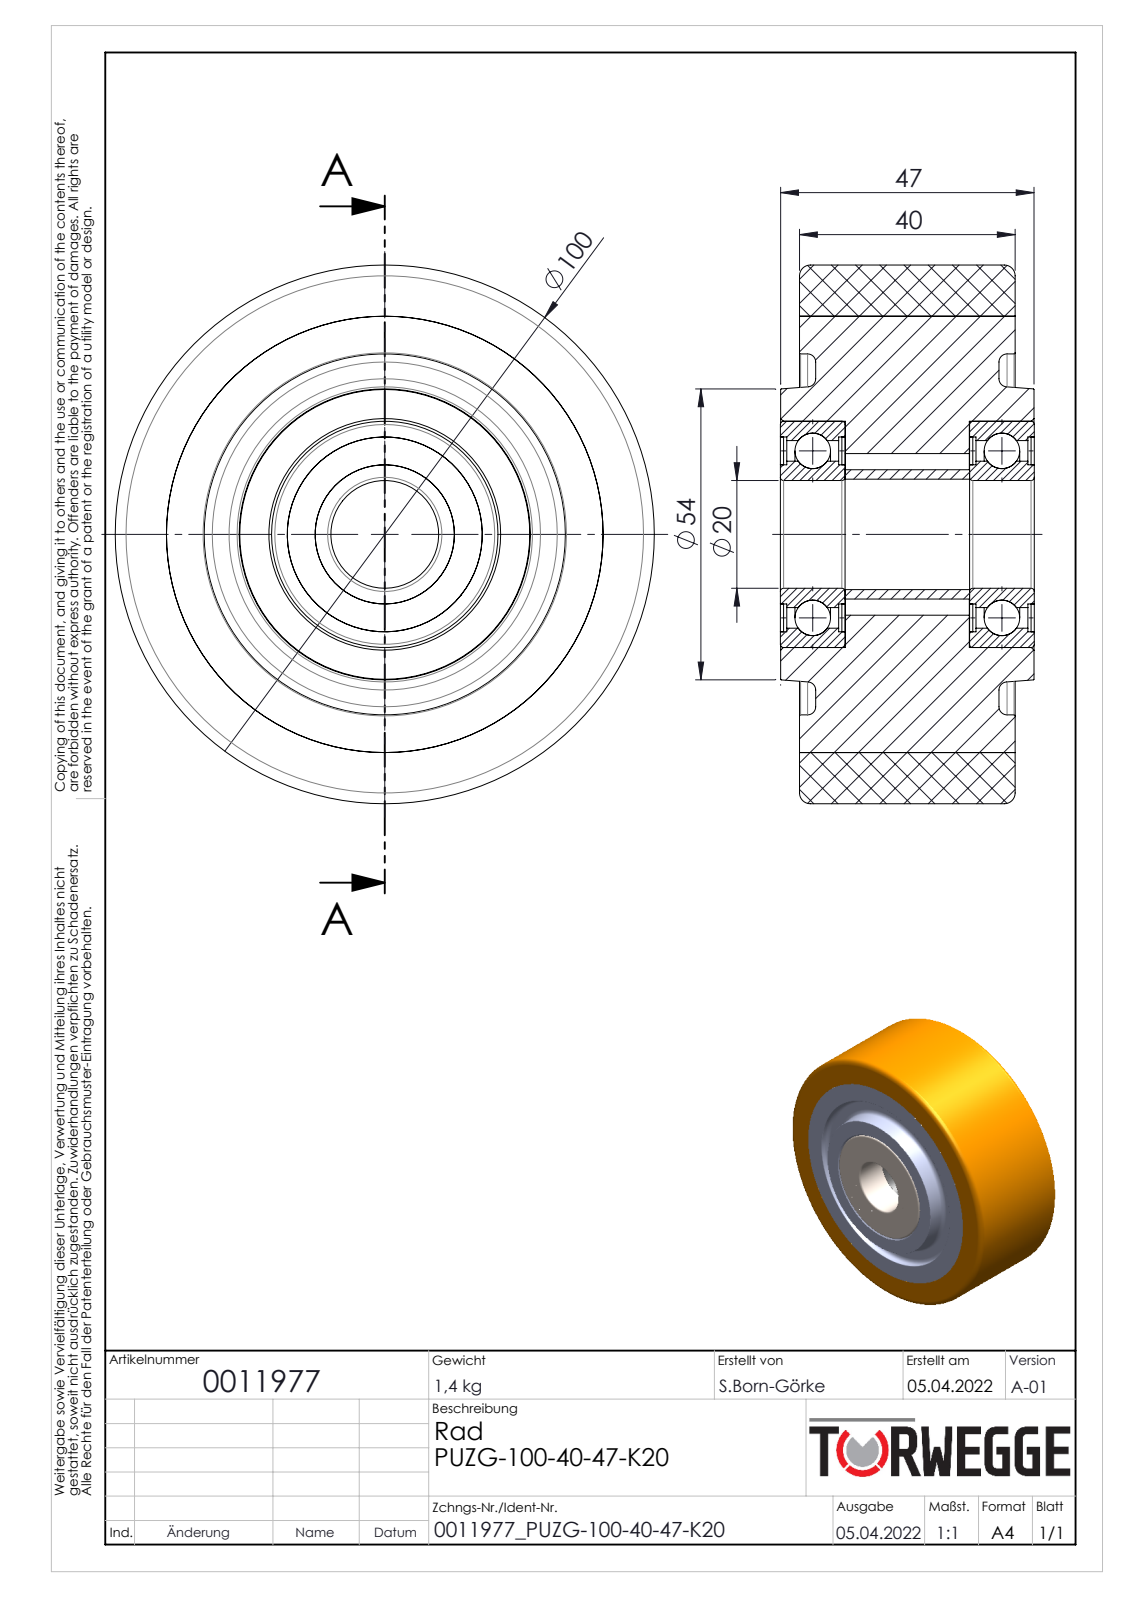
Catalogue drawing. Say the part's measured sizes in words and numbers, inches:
The part is named "0011977". Its 3-D file was written by "SolidWorks 2020 (AUTOMOTIVE_DESIGN)". It is 13 solids with 176 faces: 36 planar, 76 cylindrical and 64 other. Overall it measures 3.937 by 3.937 by 1.854 inches. Its volume is 18.21 cubic inches and its surface area 122.5 square inches. Round holes: 1 of diameter 0.787, 1 of diameter 0.807, 1 of diameter 1.017, 1 of diameter 1.181, 1 of diameter 1.371, 1 of diameter 1.424, 1 of diameter 1.654, 1 of diameter 2.638, 1 of diameter 3.189. Round bosses or shafts: 1 of diameter 3.937, 1 of diameter 1.07, 1 of diameter 0.945. The main face-to-face distances are 1.575, 0.472, 1.382, 1.38, 0.333, 1.242, 0.023, 0.449, 0.14, 1.715.
